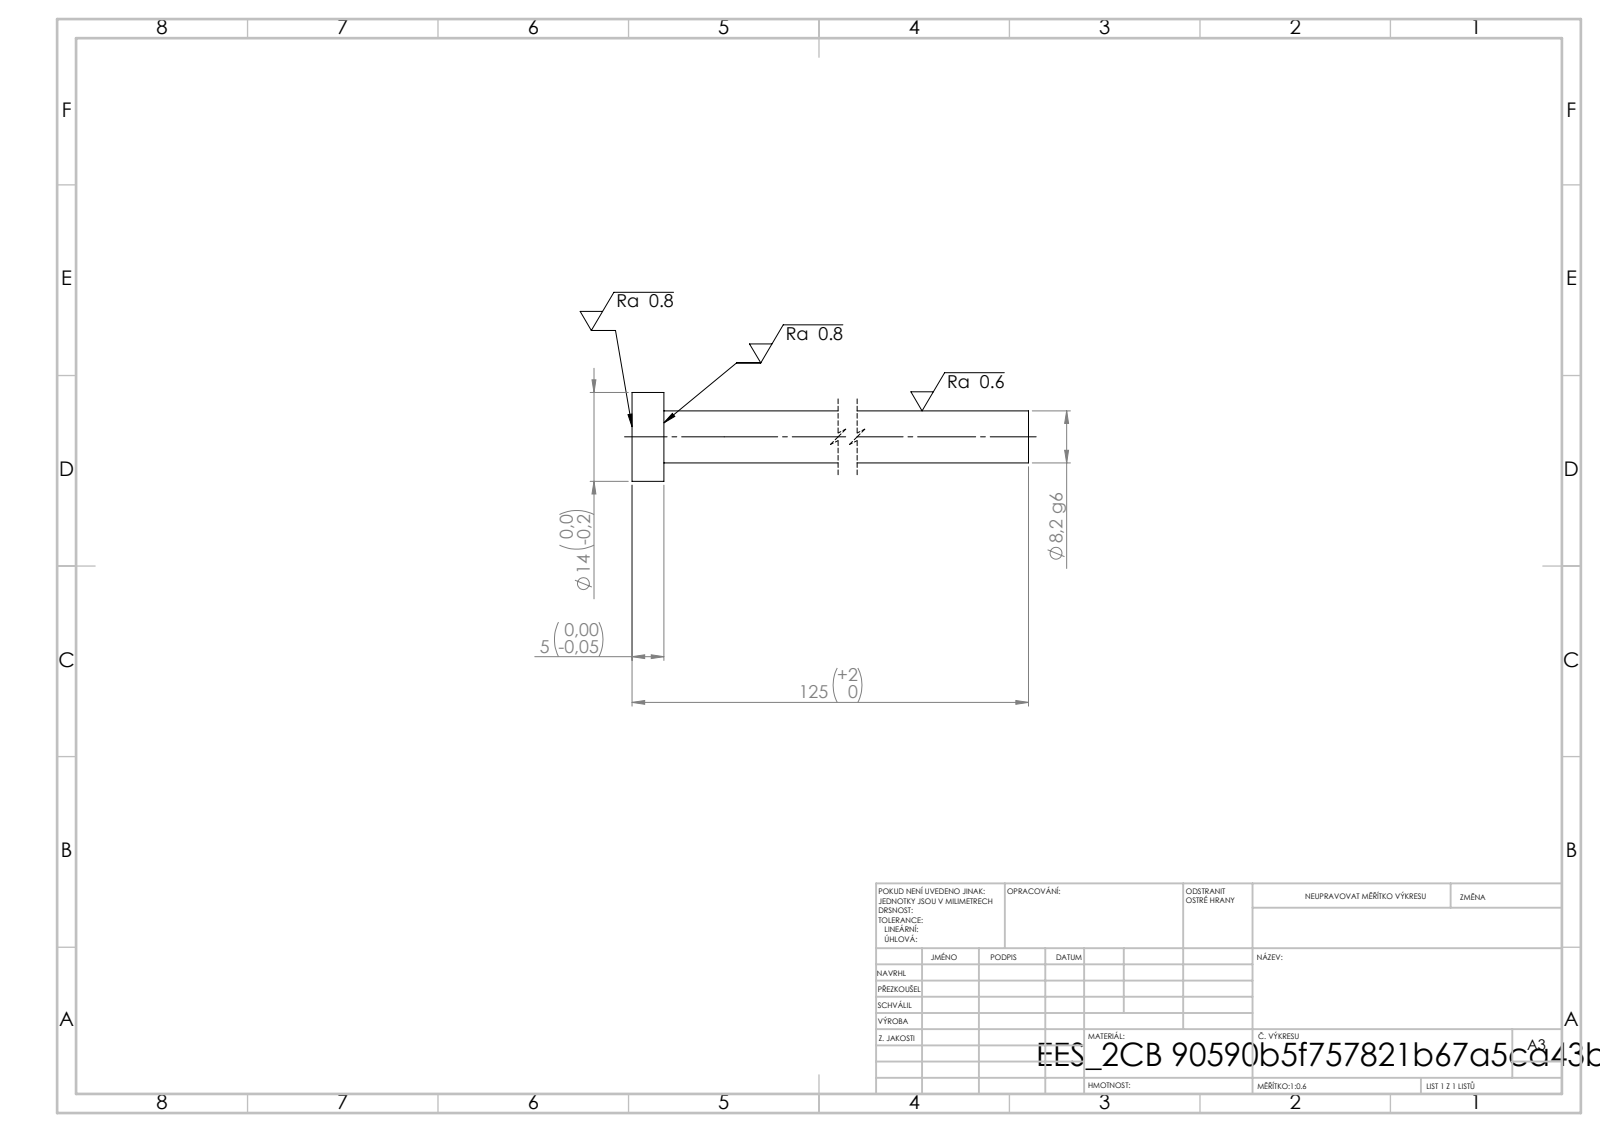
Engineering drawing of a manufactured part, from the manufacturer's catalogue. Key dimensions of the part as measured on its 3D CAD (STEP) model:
STEP written by: SolidWorks 2019 (CONFIG_CONTROL_DESIGN)
Units: millimetres
Bodies: 1 solid, 7 faces (3 planar, 4 cylindrical, 0 other)
Overall size (bounding box): 125 × 14 × 14
Volume: 7 107 mm³ · Surface area: 3 619 mm²
Round bosses / shafts (diameter × count): ⌀14 ×1, ⌀8.2 ×1
Main face-to-face distances: 5, 125, 120
